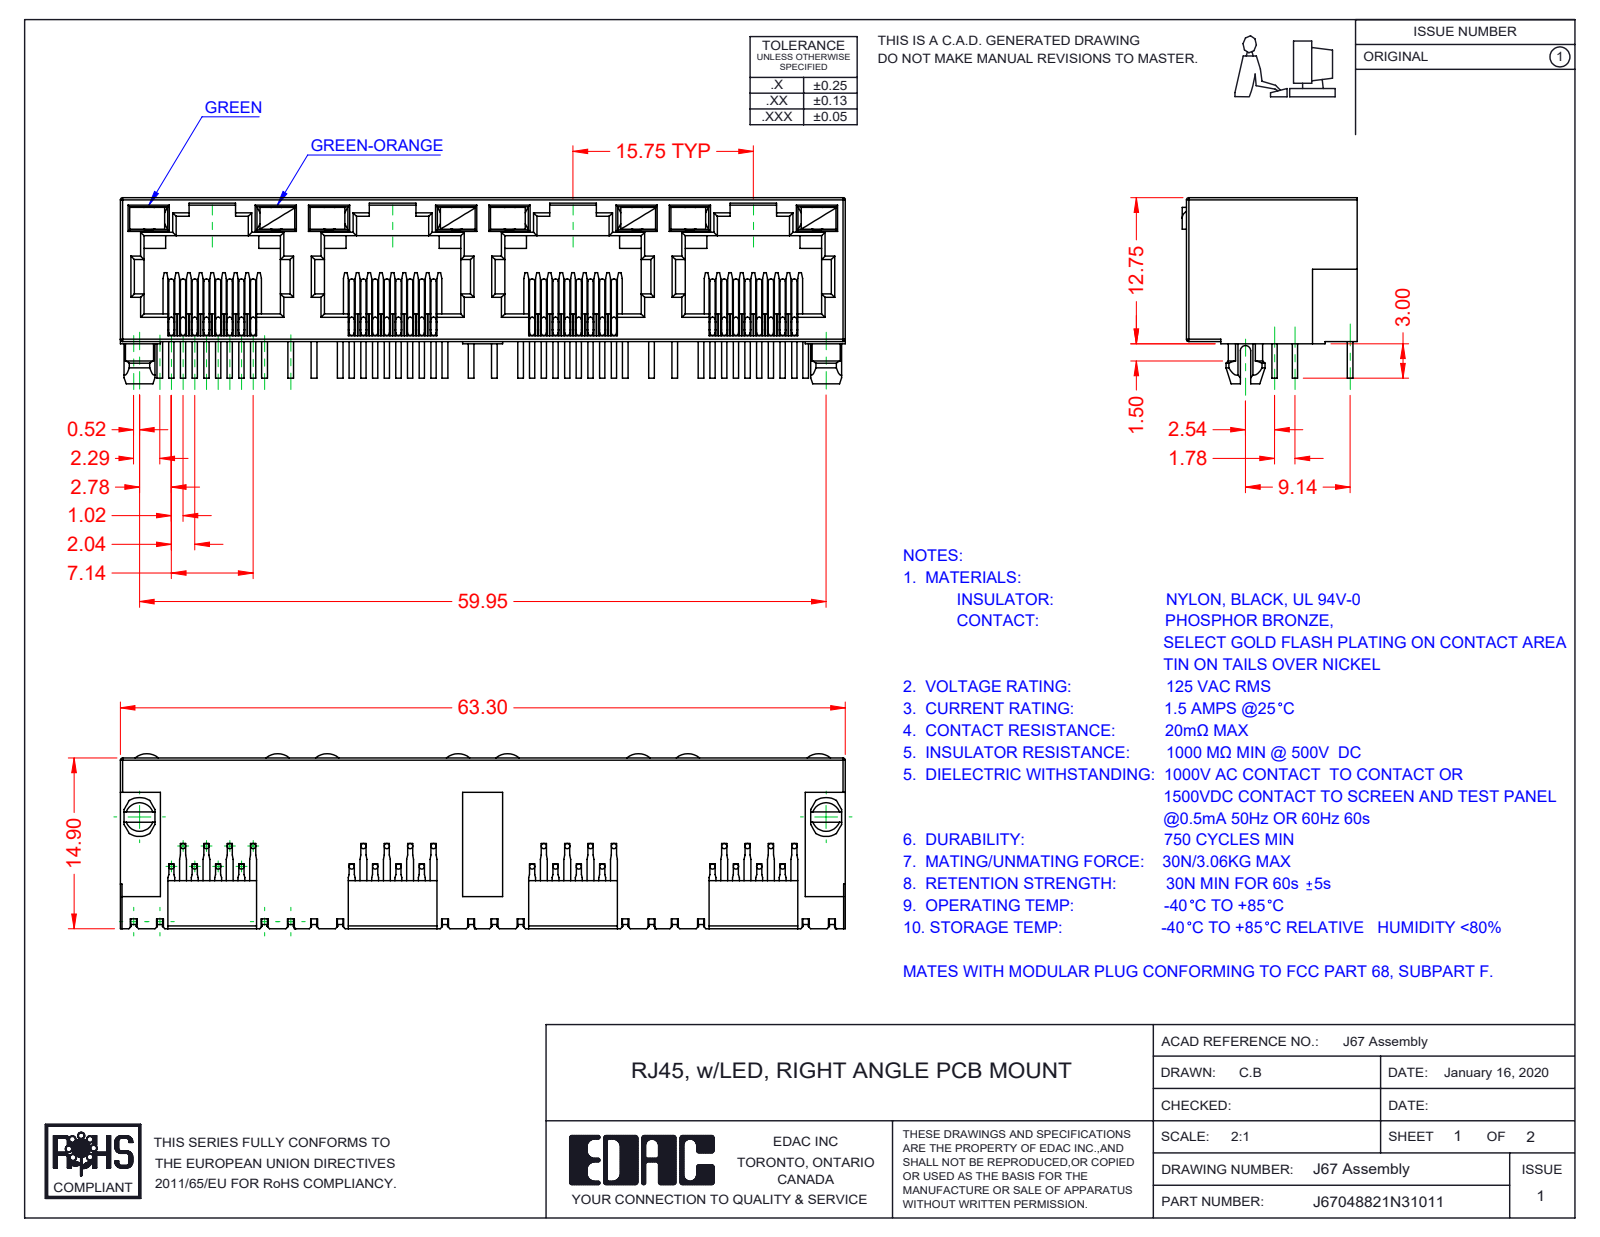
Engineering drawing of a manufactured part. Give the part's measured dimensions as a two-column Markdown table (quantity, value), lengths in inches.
| quantity | value |
| --- | --- |
| part name | 67 Contacts; 67 LED RH_7-Green-Orange; 67 Insulator; 67 LED LH_3-Green (+1 more) |
| STEP written by | SolidWorks 2016 (CONFIG_CONTROL_DESIGN) |
| units | inches |
| bodies | 41 solids, 2473 faces (1781 planar, 484 cylindrical, 208 other) |
| overall size | 2.492 × 0.64 × 0.602 |
| volume | 0.315 in³ |
| surface area | 17.94 in² |
| round bosses / shafts (diameter × count) | 0.018 × 96 |
| partial cylindrical surfaces (radius × count) | 0.008 × 66, 0.012 × 29, 0.018 × 9, 0.061 × 8, 0.059 × 2, 0.067 × 2, 0.014 × 1, 0.039 × 1 |
| main face-to-face distances | 0.02, 0.494, 0.074, 0.035, 0.394, 0.62, 0.039, 0.055, 0.433, 0.468 |
